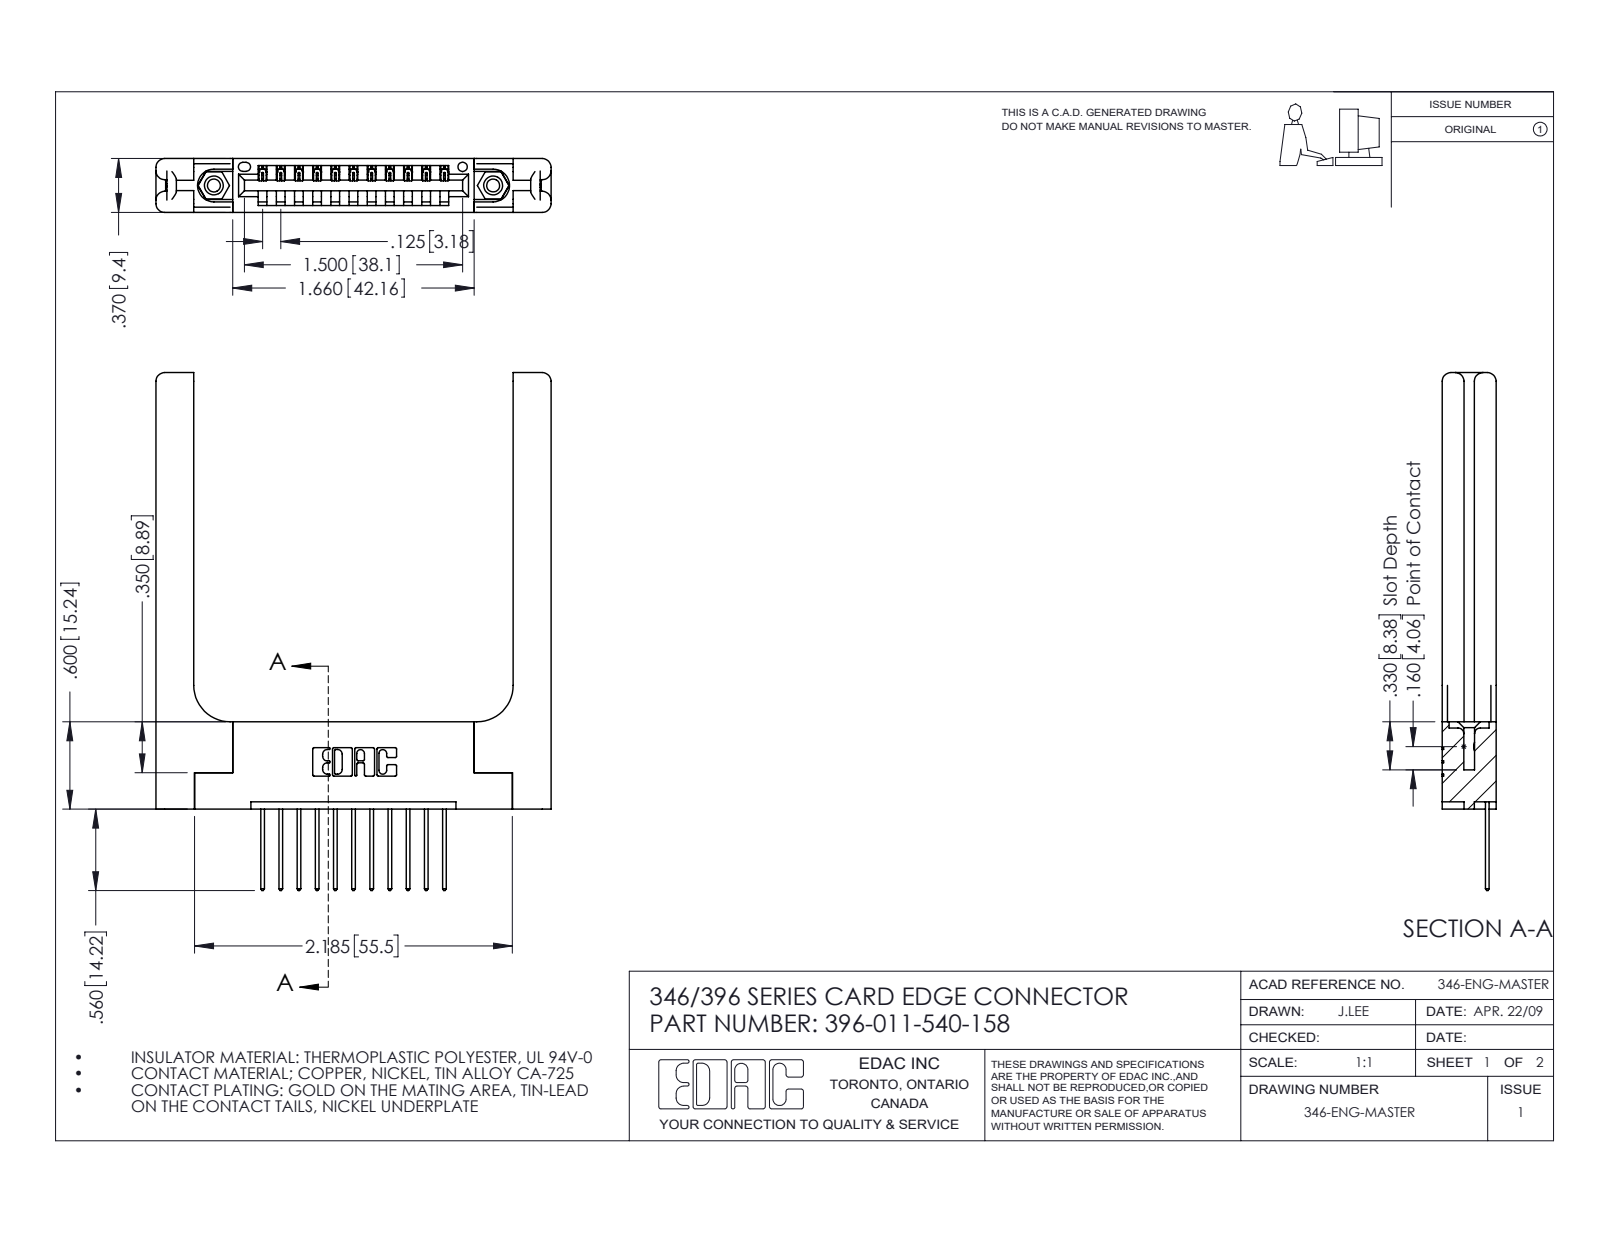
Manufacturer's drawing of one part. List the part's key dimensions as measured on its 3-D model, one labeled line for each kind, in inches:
Part name (STEP PRODUCT): 396-011-540-158; 345-292-001_345-293-140; 345-250-001_345-250-001-102; 346-220-058_345-220-058 (+1 more)
STEP written by: SolidWorks 2016 (CONFIG_CONTROL_DESIGN)
Units: inches
Bodies: 16 solids, 1016 faces (664 planar, 292 cylindrical, 60 other)
Overall size (bounding box): 3.56 × 2.716 × 0.37
Volume: 0.85 in³ · Surface area: 20.07 in²
Round holes (diameter × count): ⌀0.089 ×2, ⌀0.125 ×2, ⌀0.156 ×2, ⌀0.064 ×1
Round bosses / shafts (diameter × count): ⌀0.155 ×2
Partial cylindrical surfaces — rounded edges, fillets, slot ends (radius × count): R0.006 ×22, R0.01 ×22, R0.01 ×22, R0.06 ×16, R0.007 ×6, R0.031 ×6, R0.026 ×3, R0.03 ×2
Main face-to-face distances: 0.37, 0.15, 0.072, 0.148, 0.22, 0.048, 0.322, 0.25, 0.102, 0.173
Hole centre spacings: 0.246, 1.715, 1.92
